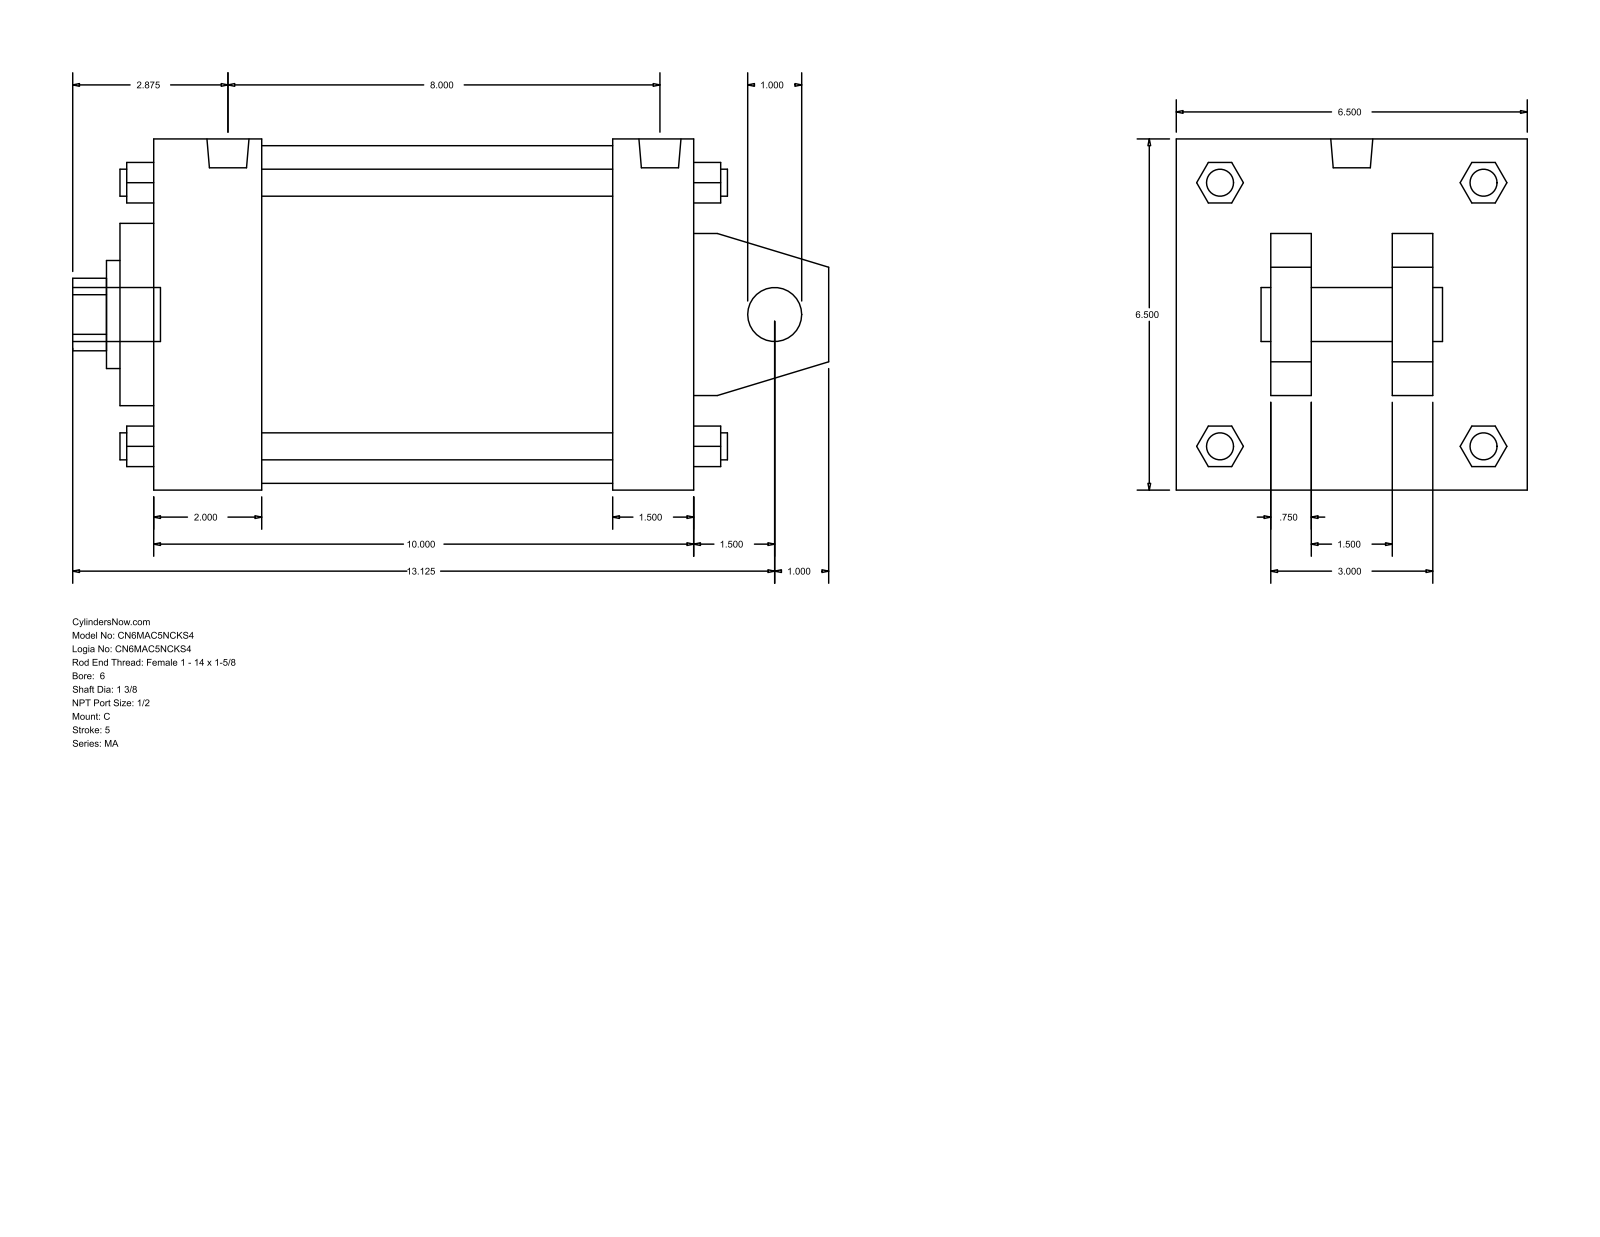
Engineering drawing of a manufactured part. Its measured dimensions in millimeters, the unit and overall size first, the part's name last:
Units: millimetres
Overall size (bounding box): 355.6 × 165.1 × 165.1
Round holes (diameter × count): ⌀25.4 ×1, ⌀34.92 ×1, ⌀50.8 ×1, ⌀85.72 ×1, ⌀158.75 ×1
Round bosses / shafts (diameter × count): ⌀17.46 ×4, ⌀12.7 ×4, ⌀19.77 ×2, ⌀25.4 ×1
Partial cylindrical surfaces — rounded edges, fillets, slot ends (radius × count): R17.06 ×1
Main face-to-face distances: 165.1, 254, 38.1, 19.05, 63.5, 101.6, 50.8, 44.45, 120.65, 215.9
Bodies: 0 solids, 141 faces (109 planar, 32 cylindrical, 0 other)
Part name (STEP PRODUCT): MA_C__0600_1.375
STEP written by: GSSL Pune (CONFIG_CONTROL_DESIGN)
